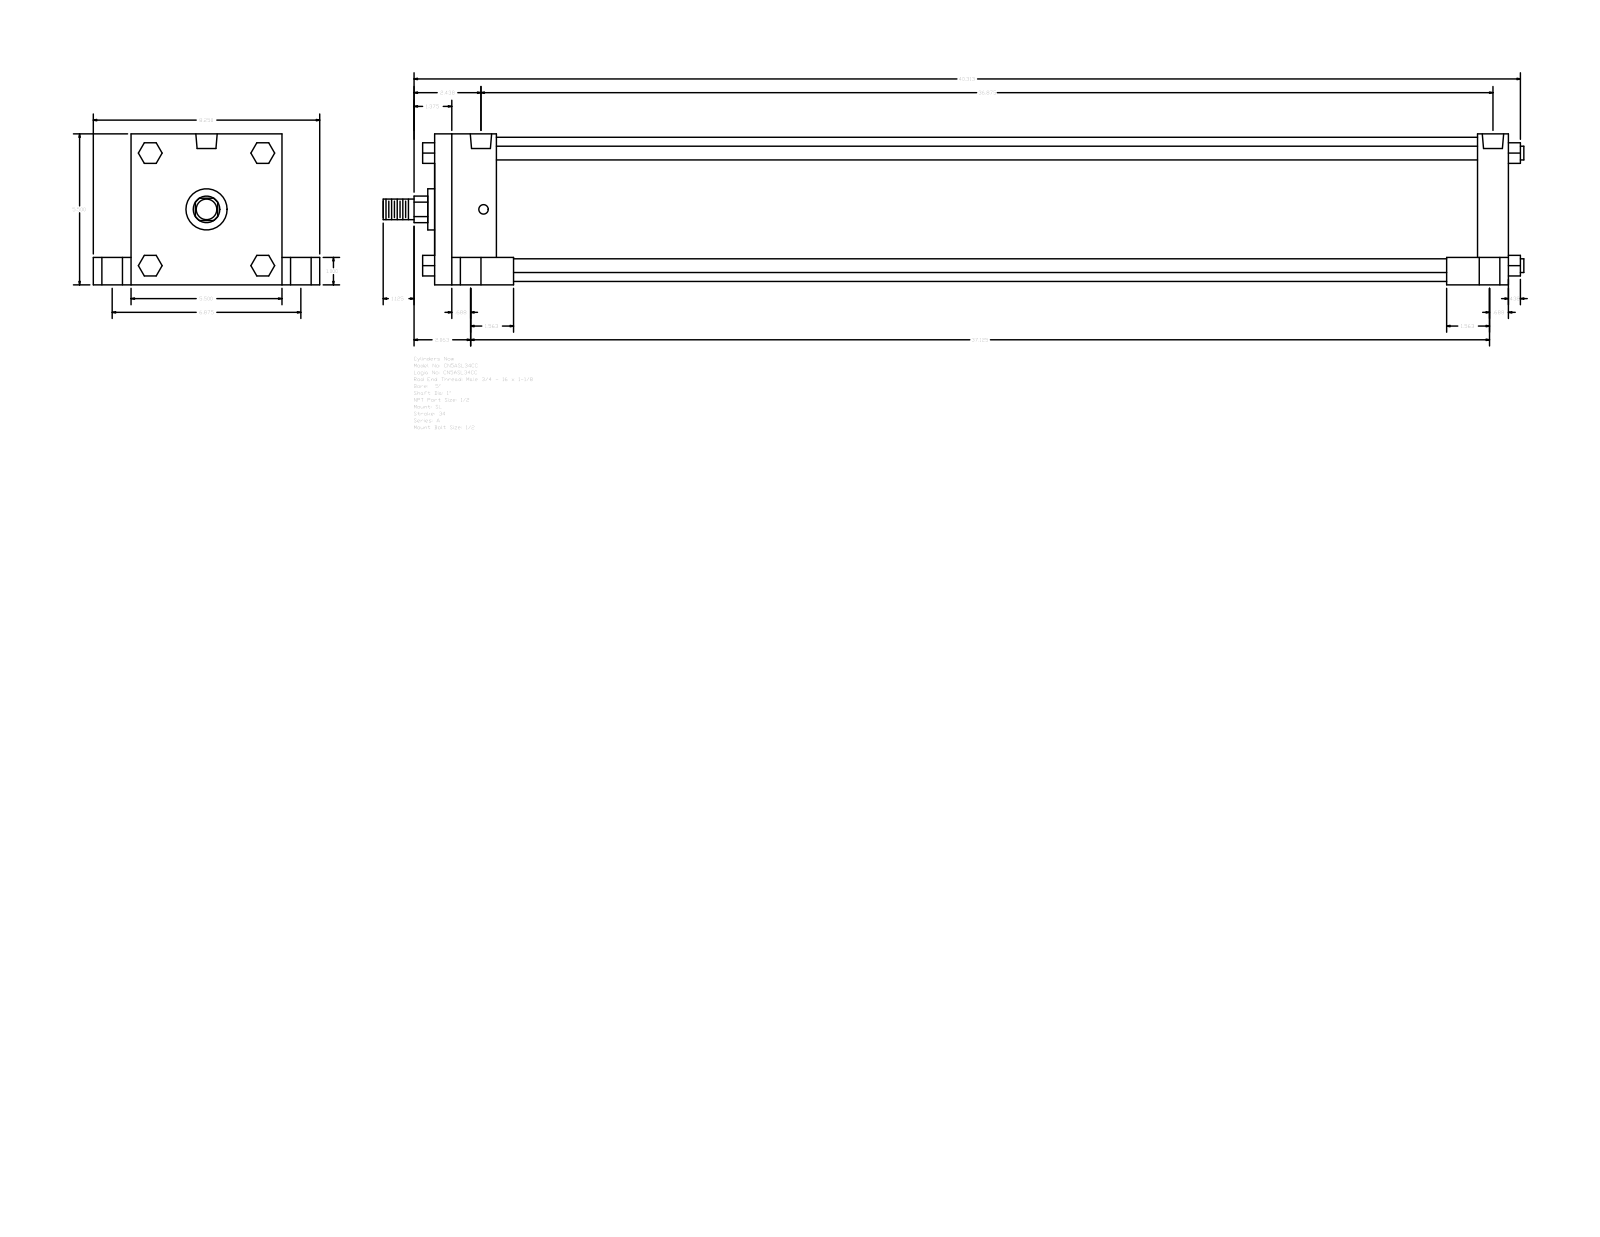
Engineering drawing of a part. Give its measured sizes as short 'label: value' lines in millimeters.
name: A_SL__0500_1
written by: GSSL Pune (CONFIG_CONTROL_DESIGN)
unit: mm
bodies: 0 solids, 150 faces (114 planar, 36 cylindrical, 0 other)
size: 1055.69 × 209.55 × 139.7
holes: 4× ⌀8.73, 4× ⌀19.05, 4× ⌀25.4, 2× ⌀19.77
bosses: 4× ⌀12.7, 1× ⌀133.35, 1× ⌀38.1, 1× ⌀25.4, 1× ⌀19.05
rounds: 1× R12.29
face distances: 139.7, 993.78, 28.58, 25.4, 114.3, 34.93, 174.63, 57.15, 965.2, 908.05
hole spacings: 2.39, 87.31, 87.37, 87.83, 88.12, 174.62, 931.85, 934.24
